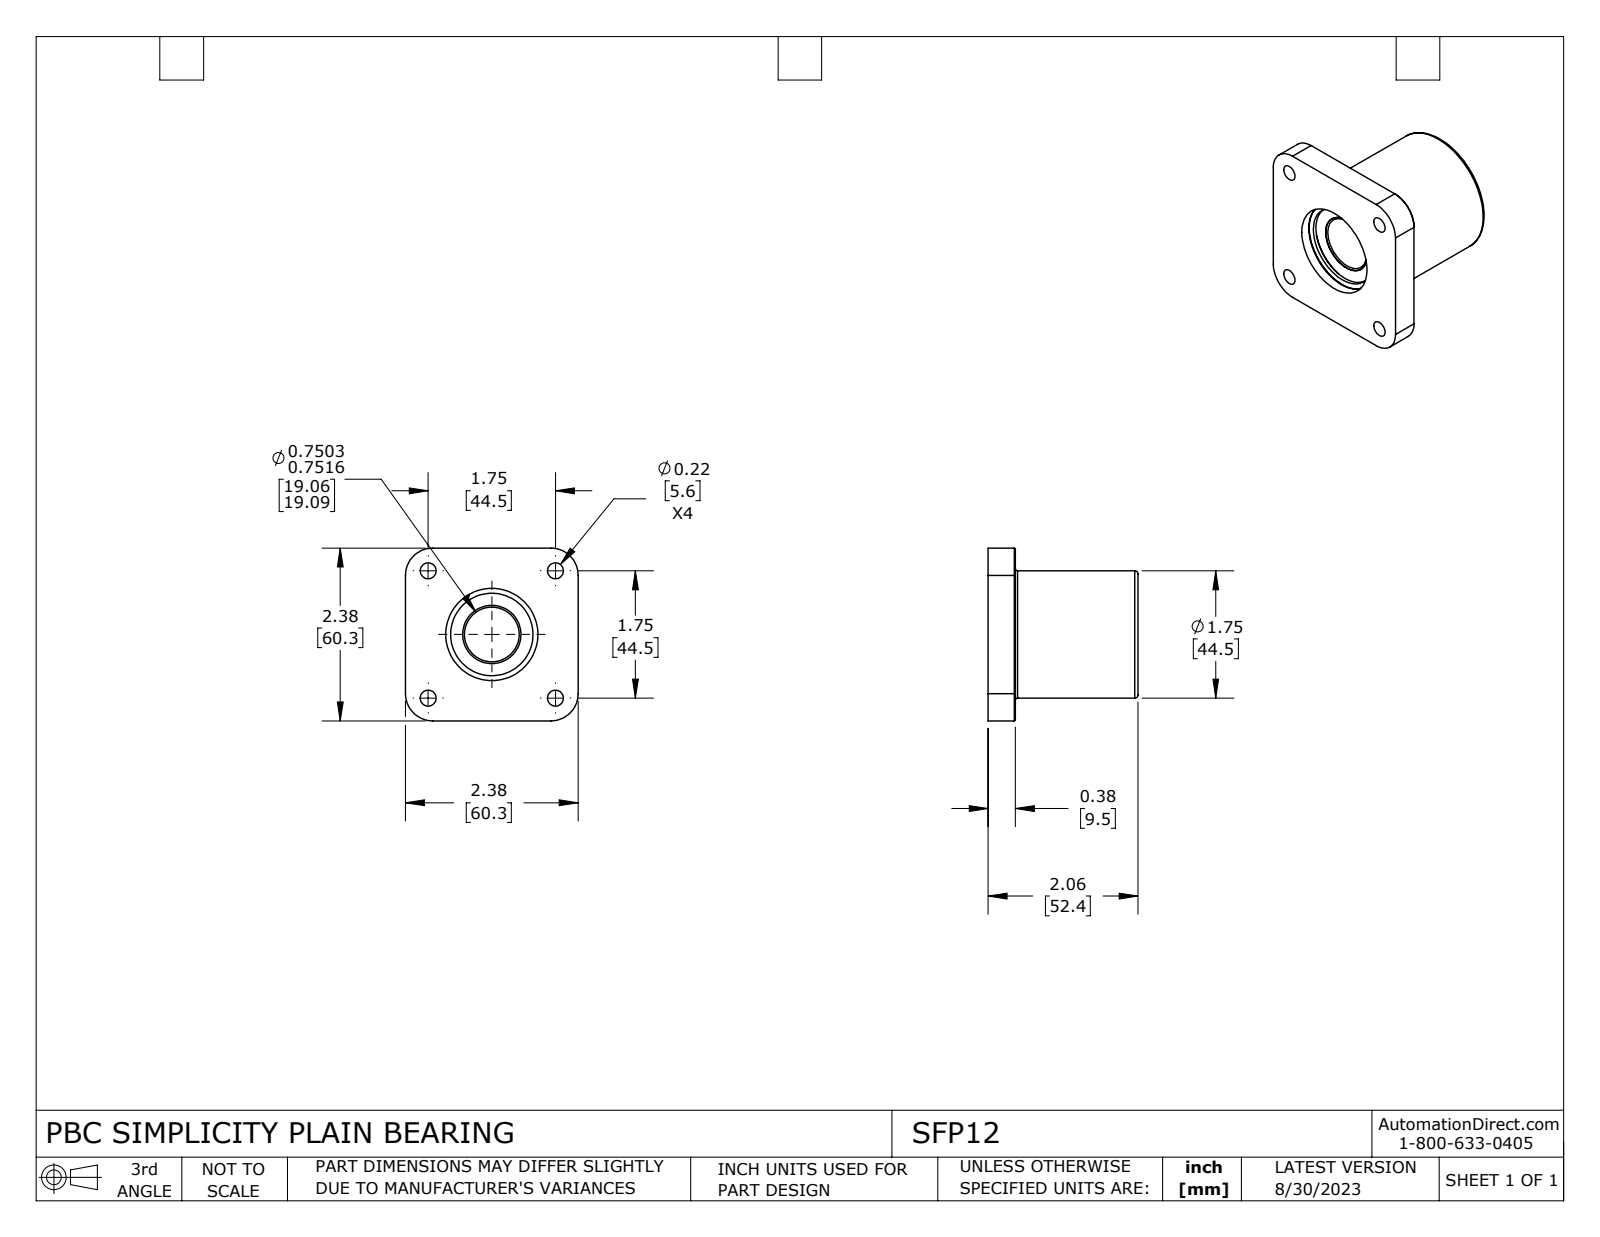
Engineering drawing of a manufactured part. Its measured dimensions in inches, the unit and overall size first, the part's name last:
Units: inches
Overall size (bounding box): 2.375 × 2.375 × 2.062
Round holes (diameter × count): ⌀0.219 ×4, ⌀0.751 ×1, ⌀0.802 ×1, ⌀1.133 ×1, ⌀1.267 ×1, ⌀1.332 ×1
Round bosses / shafts (diameter × count): ⌀1.75 ×1, ⌀1.339 ×1, ⌀1.249 ×1, ⌀1.177 ×1, ⌀1.087 ×1
Partial cylindrical surfaces — rounded edges, fillets, slot ends (radius × count): R0.017 ×4, R0.375 ×4, R0.012 ×2, R0.022 ×2
Main face-to-face distances: 0.375, 2.375, 0.158, 1.904, 0.208, 1.854, 0.05, 1.696, 2.062, 1.687
Hole centre spacings: 1.238, 1.75, 2.476
Volume: 4.741 in³ · Surface area: 56.18 in²
Bodies: 7 solids, 169 faces (41 planar, 74 cylindrical, 54 other)
Part name (STEP PRODUCT): SFP12
STEP written by: SolidWorks 2021 (CONFIG_CONTROL_DESIGN)
